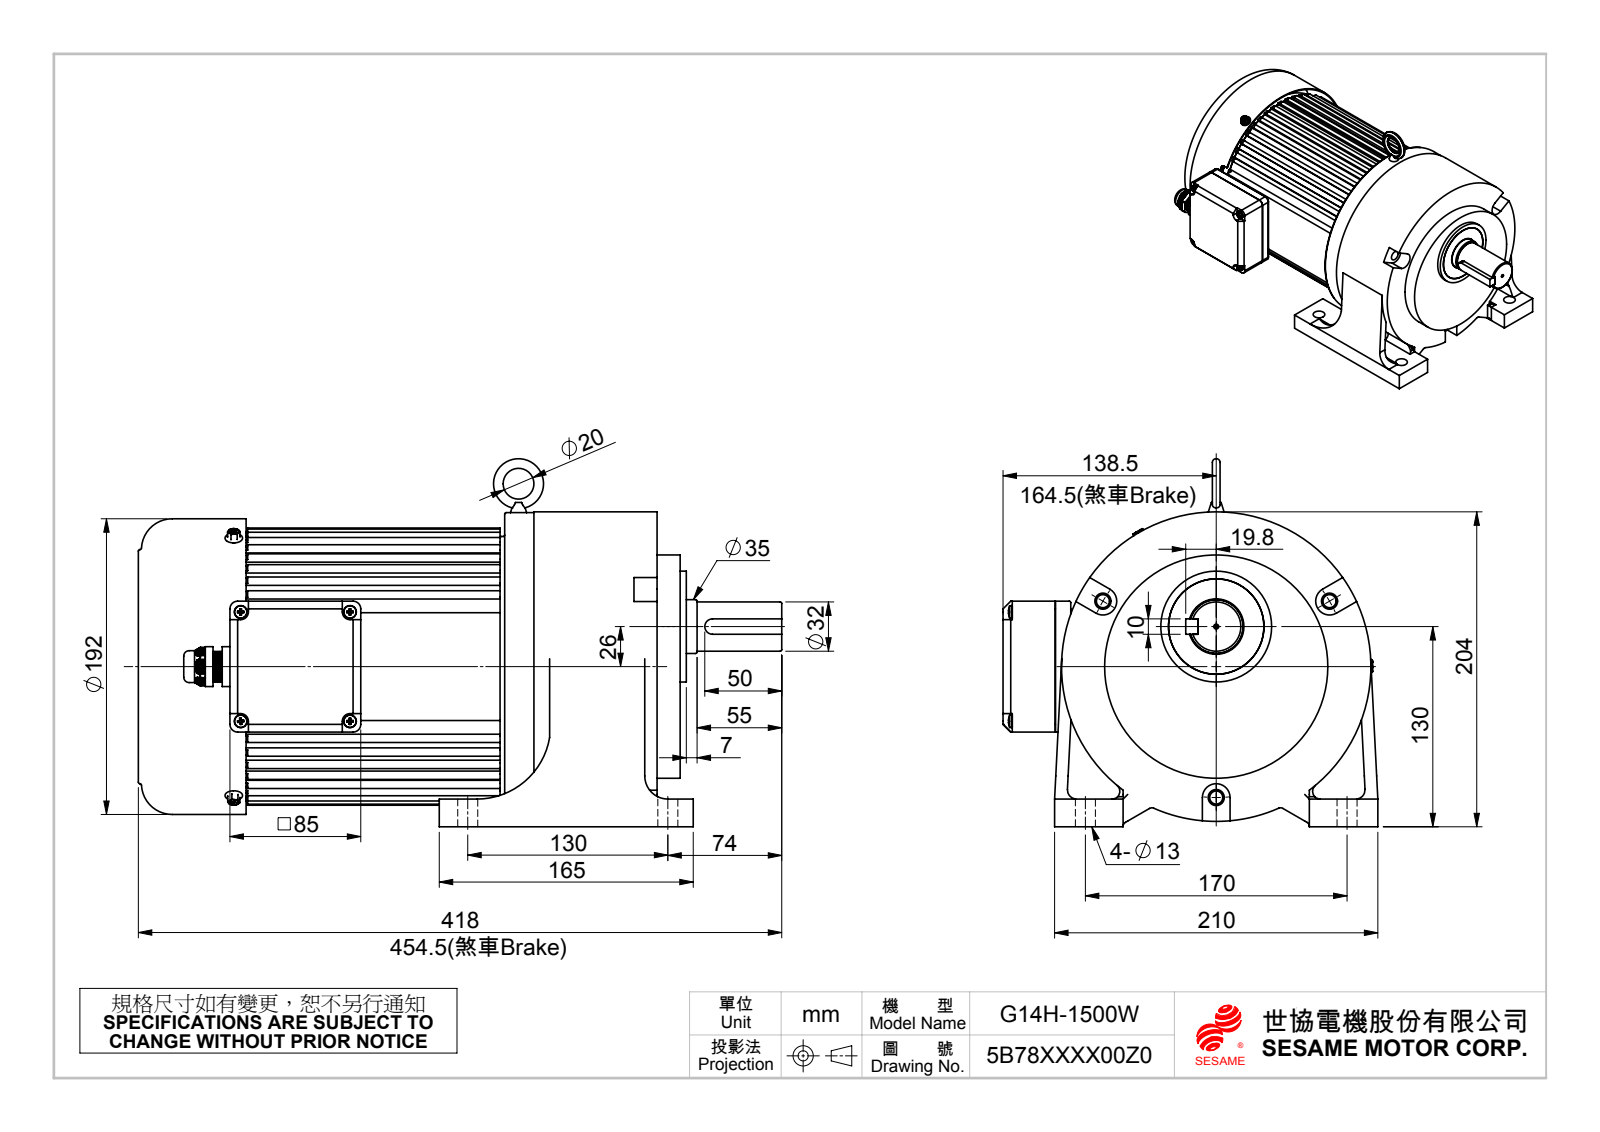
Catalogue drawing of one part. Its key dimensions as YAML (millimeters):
part_name: "出線盒墊片JTH-UP3(PVC2mm厚); 出線盒上蓋; G140S1; 10x8xL_50L (+8 more)"
step_written_by: "SolidWorks 2010 (CONFIG_CONTROL_DESIGN)"
units: millimeters
bodies: {solids: 20, faces: 3151, planar: 1195, cylindrical: 899, other: 1057}
overall_size: [418, 243.5, 239]
volume: 8565000
surface_area: 732177
round_holes:
  - {diameter: 5, count: 11}
  - {diameter: 3.3, count: 9}
  - {diameter: 6, count: 4}
  - {diameter: 8, count: 4}
  - {diameter: 13, count: 4}
  - {diameter: 4.2, count: 3}
  - {diameter: 10.5, count: 3}
  - {diameter: 15, count: 3}
  - {diameter: 2, count: 1}
  - {diameter: 6.5, count: 1}
  - {diameter: 6.8, count: 1}
  - {diameter: 10.8, count: 1}
round_bosses_or_shafts:
  - {diameter: 8.3, count: 4}
  - {diameter: 4, count: 4}
  - {diameter: 5, count: 3}
  - {diameter: 201, count: 1}
  - {diameter: 200, count: 1}
  - {diameter: 192, count: 1}
  - {diameter: 190, count: 1}
  - {diameter: 171, count: 1}
partial_cylinders:
  - {radius: 2.25, count: 42}
  - {radius: 0.5, count: 24}
  - {radius: 1, count: 24}
  - {radius: 3, count: 12}
  - {radius: 5, count: 11}
  - {radius: 2.9, count: 6}
  - {radius: 2, count: 4}
  - {radius: 2.55, count: 4}
face_to_face_distances: [195, 2, 168, 27, 18, 9.5, 177.5, 204.5, 175.5, 166]
hole_center_spacings: [45, 58.25, 71, 82.38, 85, 147.22, 11, 11.5]
